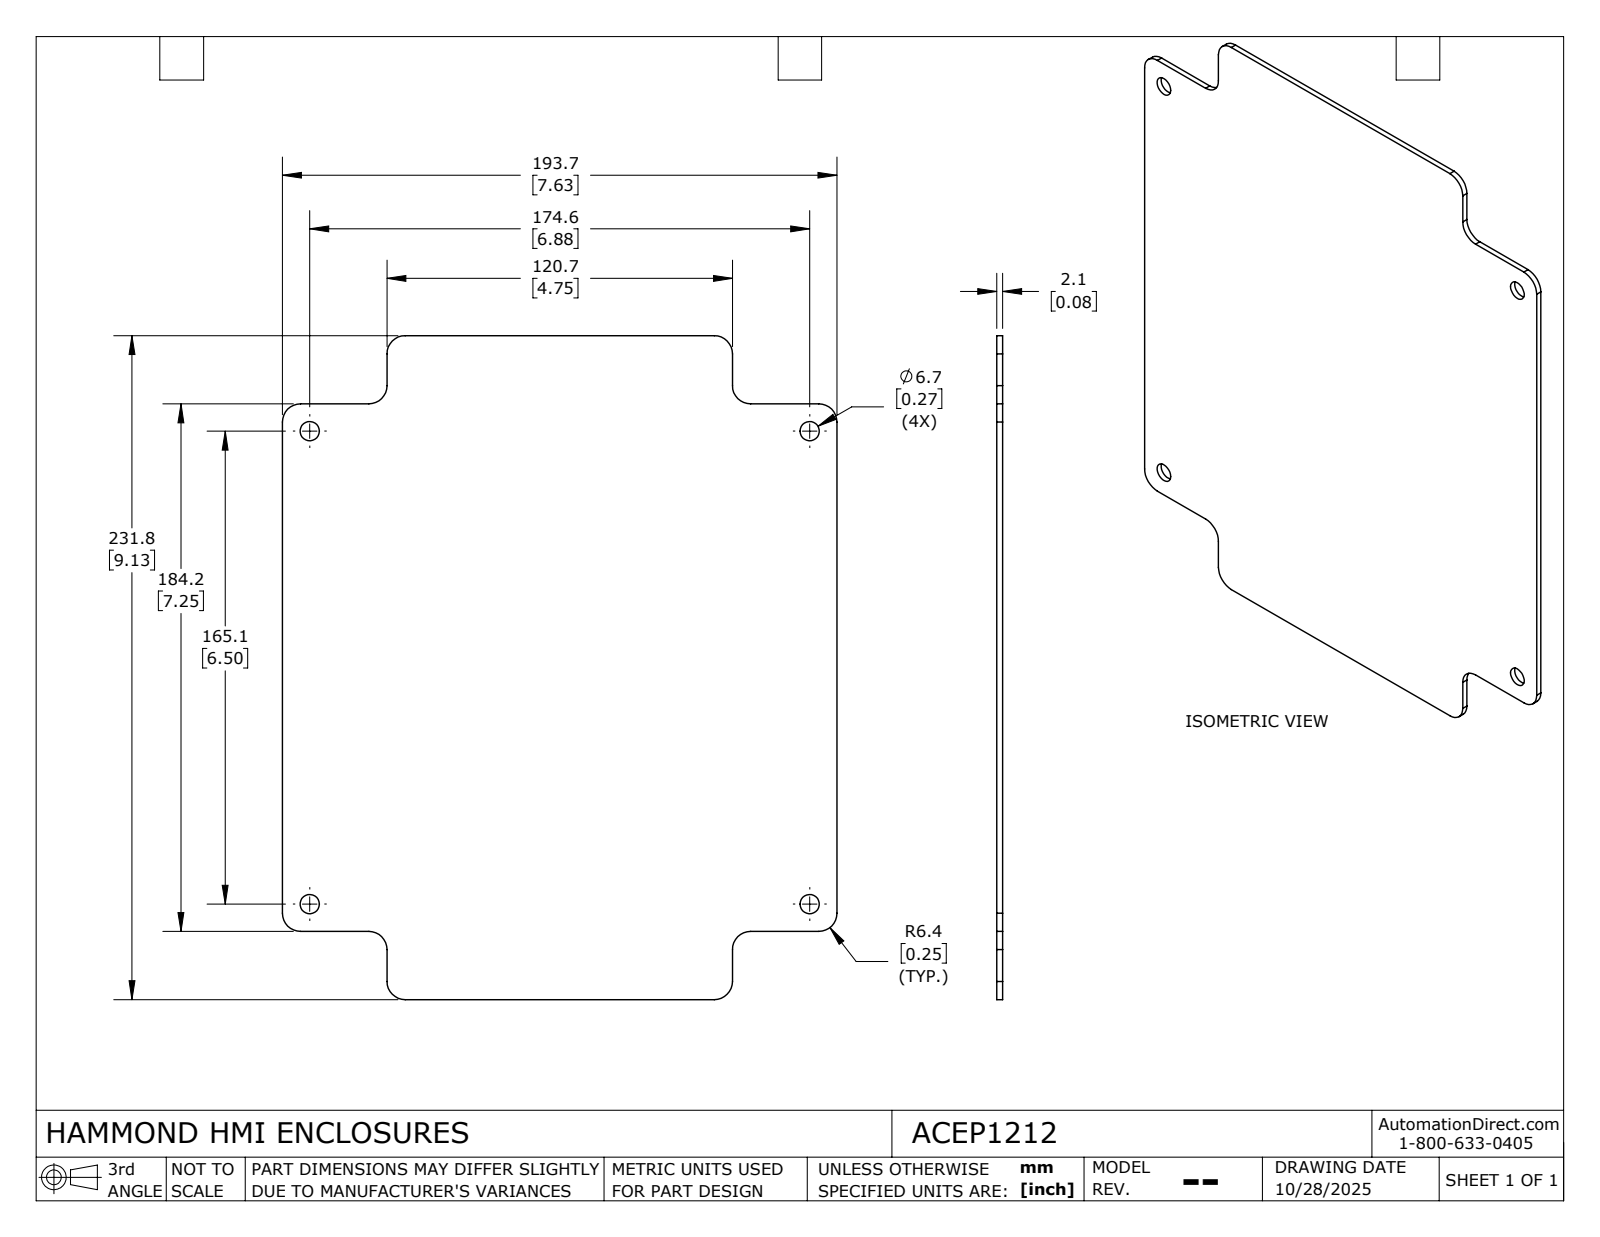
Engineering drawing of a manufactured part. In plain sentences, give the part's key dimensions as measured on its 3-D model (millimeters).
The part is named "ACEP1212". Its 3-D file was written by "SolidWorks 2024 (AUTOMOTIVE_DESIGN)". It is 1 solid with 30 faces: 14 planar, 16 cylindrical and 0 other. Overall it measures 231.78 by 193.68 by 2.06 millimeters. Its volume is 84 835 cubic millimeters and its surface area 84 326 square millimeters. Round holes: 4 of diameter 6.73. Partial cylindrical surfaces (rounded edges, fillets, slot ends): 12 of radius 6.35. The main face-to-face distances are 2.06, 193.68, 231.78, 23.81, 207.97, 184.16, 36.52, 157.16, 120.64. The hole center spacings are 165.1, 174.62, 240.31.
